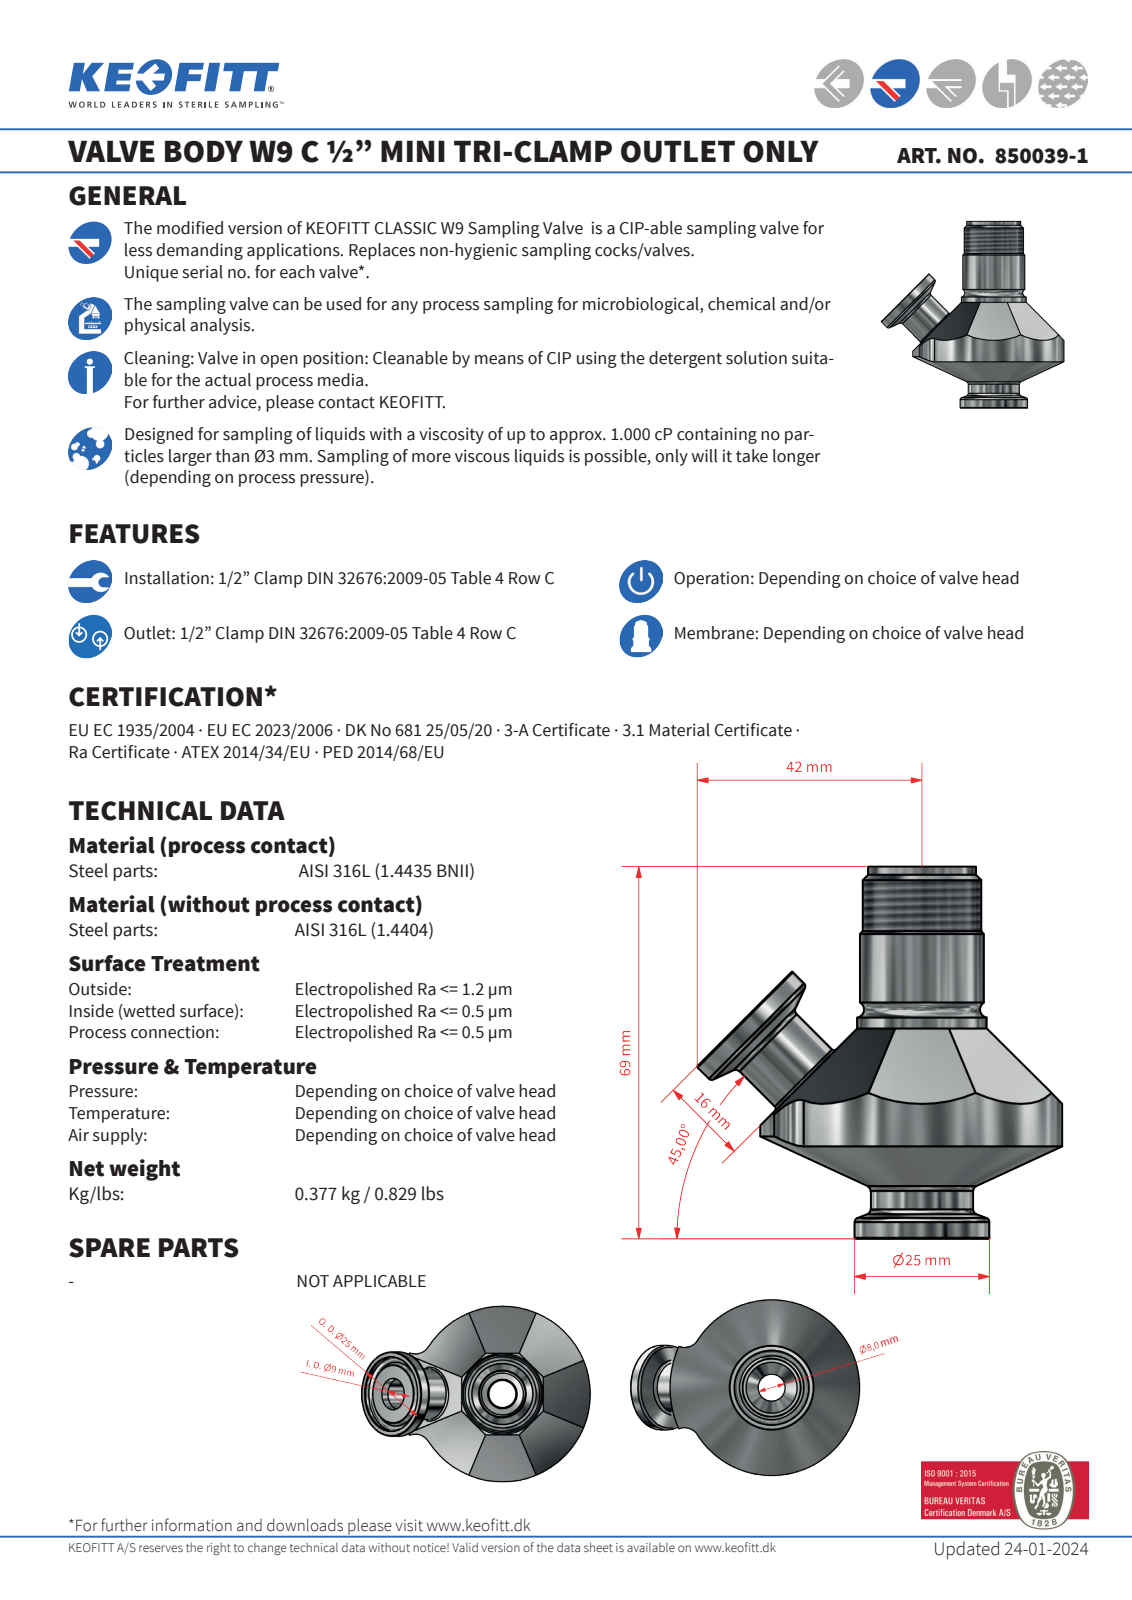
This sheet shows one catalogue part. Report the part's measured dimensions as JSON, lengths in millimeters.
{"part_name": "850039-1", "step_written_by": "Autodesk Inventor 2022 (AUTOMOTIVE_DESIGN)", "units": "millimeters", "bodies": {"solids": 1, "faces": 45, "planar": 12, "cylindrical": 12, "other": 21}, "overall_size": [69, 67.67, 52], "volume_mm3": 62587, "surface_area_mm2": 11125, "round_bosses_or_shafts": [[25, 2], [52, 1], [24, 1], [23, 1], [22, 1], [20, 1], [19, 1], [15, 1]], "partial_cylinders_radius": [[4.5, 2], [30, 1]], "face_to_face_distances": [69, 16, 39, 30]}
